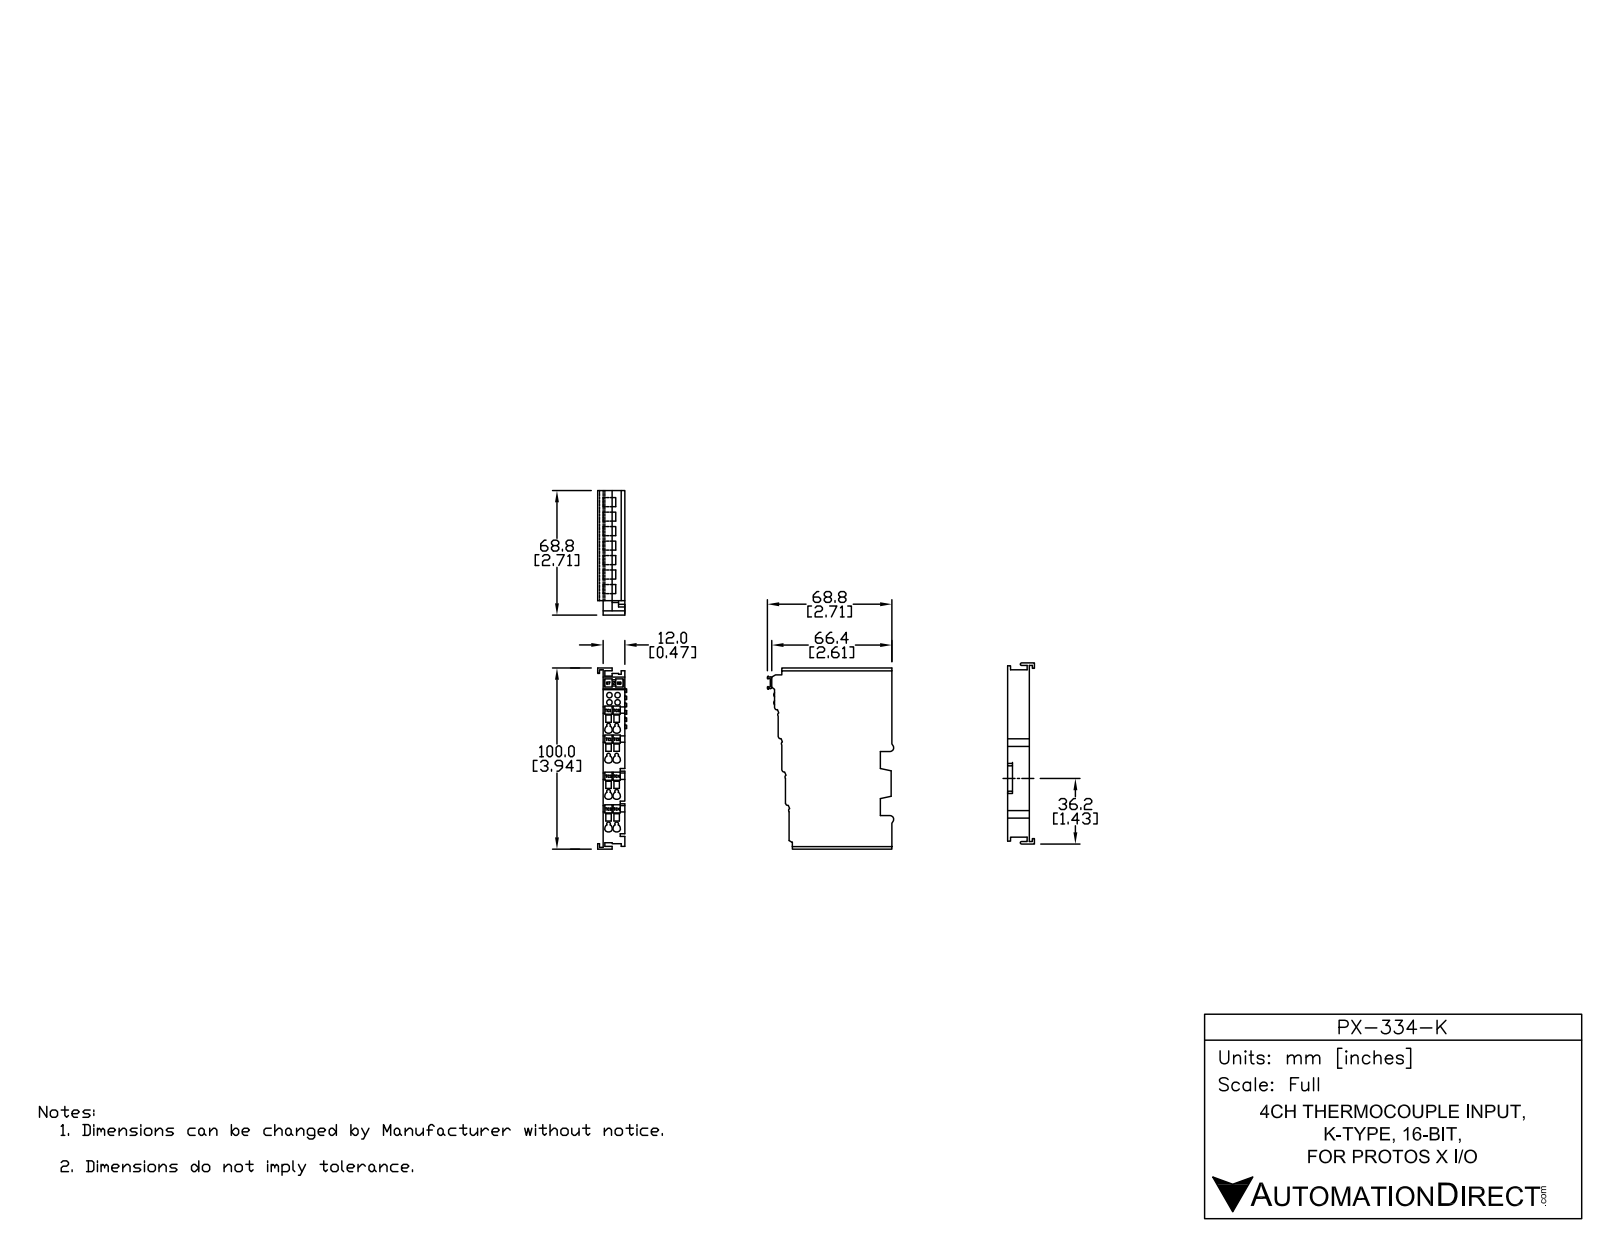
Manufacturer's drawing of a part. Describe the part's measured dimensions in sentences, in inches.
The part is named "PX-334-K". Its 3-D file was written by "SolidWorks 2014 (AUTOMOTIVE_DESIGN)". It is 28 solids with 1367 faces: 963 planar, 344 cylindrical and 60 other. Overall it measures 3.947 by 2.806 by 0.596 inches. Its volume is 3.564 cubic inches and its surface area 52.52 square inches. Round holes: 8 of diameter 0.157, 4 of diameter 0.138. Partial cylindrical surfaces (rounded edges, fillets, slot ends): 46 of radius 0.012, 35 of radius 0.01, 12 of radius 0.015, 10 of radius 0.005, 9 of radius 0.039, 8 of radius 0.016, 4 of radius 0.007, 4 of radius 0.041. The main face-to-face distances are 0.472, 0.039, 0.079, 0.394, 0.073, 0.433, 0.343, 0.157, 0.124, 0.048. The hole center spacings are 0.177, 0.197, 0.724, 0.751, 0.25, 0.63, 0.66, 0.804.
